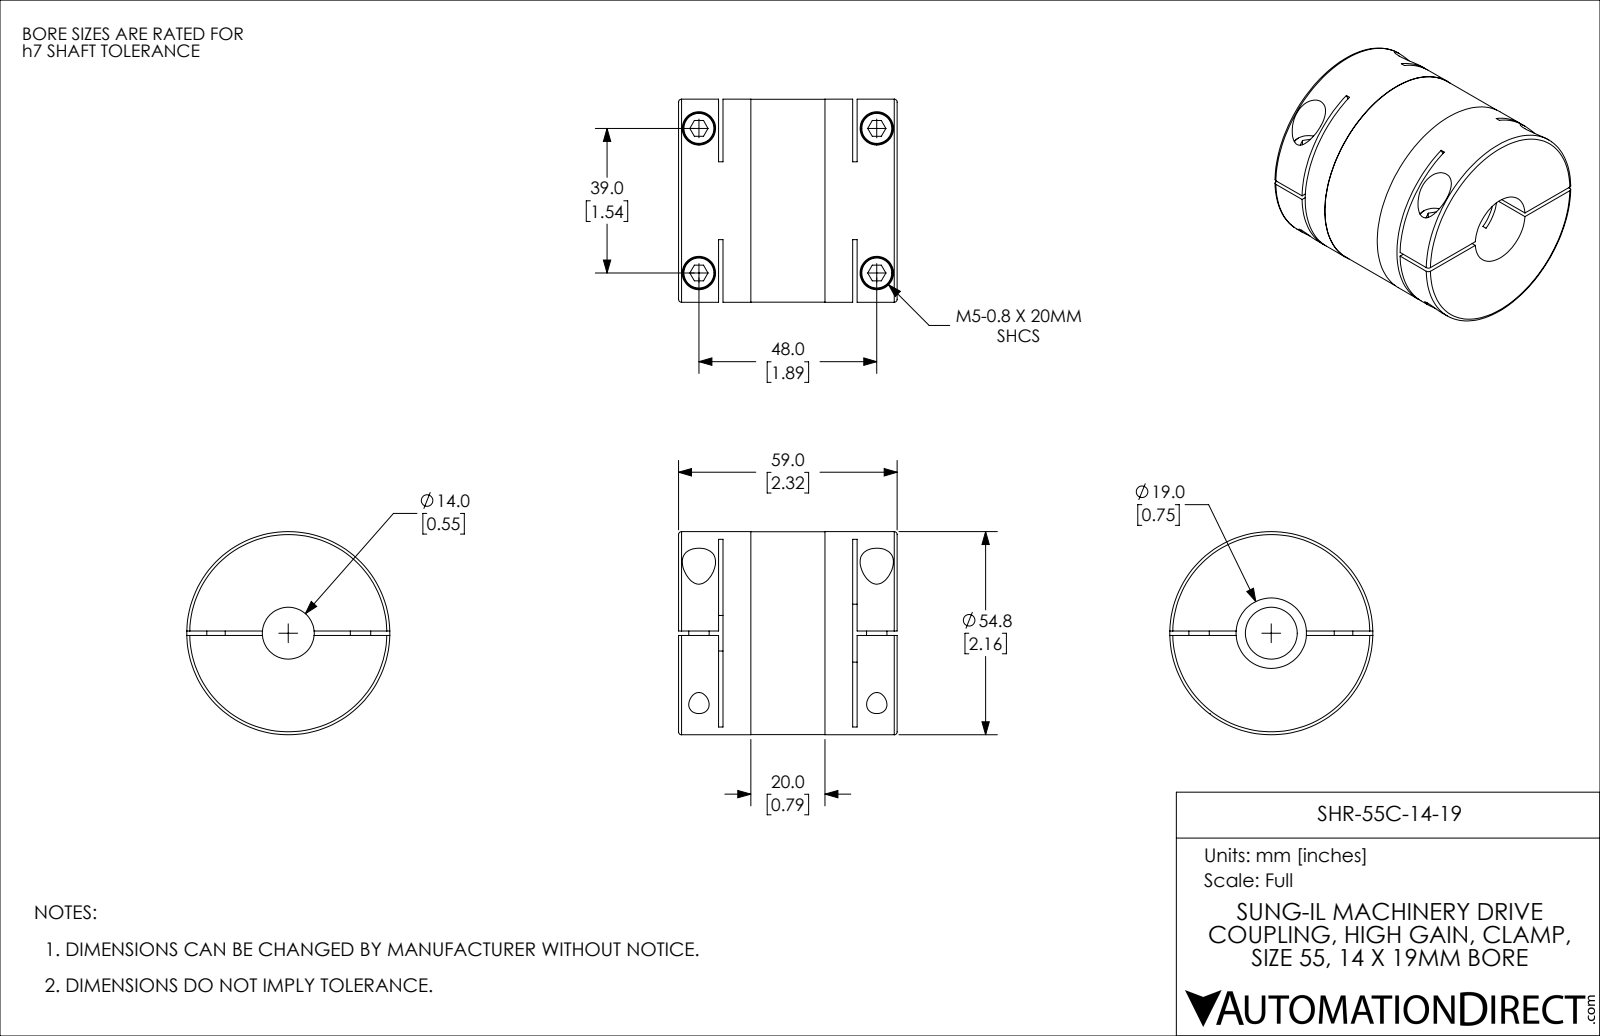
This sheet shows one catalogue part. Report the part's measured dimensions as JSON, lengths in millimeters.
{"part_name": "SHR-55C-14-19", "step_written_by": "SolidWorks 2021 (CONFIG_CONTROL_DESIGN)", "units": "millimeters", "bodies": {"solids": 1, "faces": 144, "planar": 70, "cylindrical": 58, "other": 16}, "overall_size": [59, 54.8, 54.8], "volume_mm3": 116051, "surface_area_mm2": 28698, "round_holes": [[5.5, 4], [9, 4], [14, 1], [19, 1], [21, 1]], "round_bosses_or_shafts": [[8.5, 4], [5, 2], [54.8, 1], [54.7, 1]], "partial_cylinders_radius": [[60, 2]], "face_to_face_distances": [1.2, 12, 47, 10.8, 48.2, 36.2, 59, 35, 37.4, 19.5], "hole_center_spacings": [39, 48, 61.85]}
